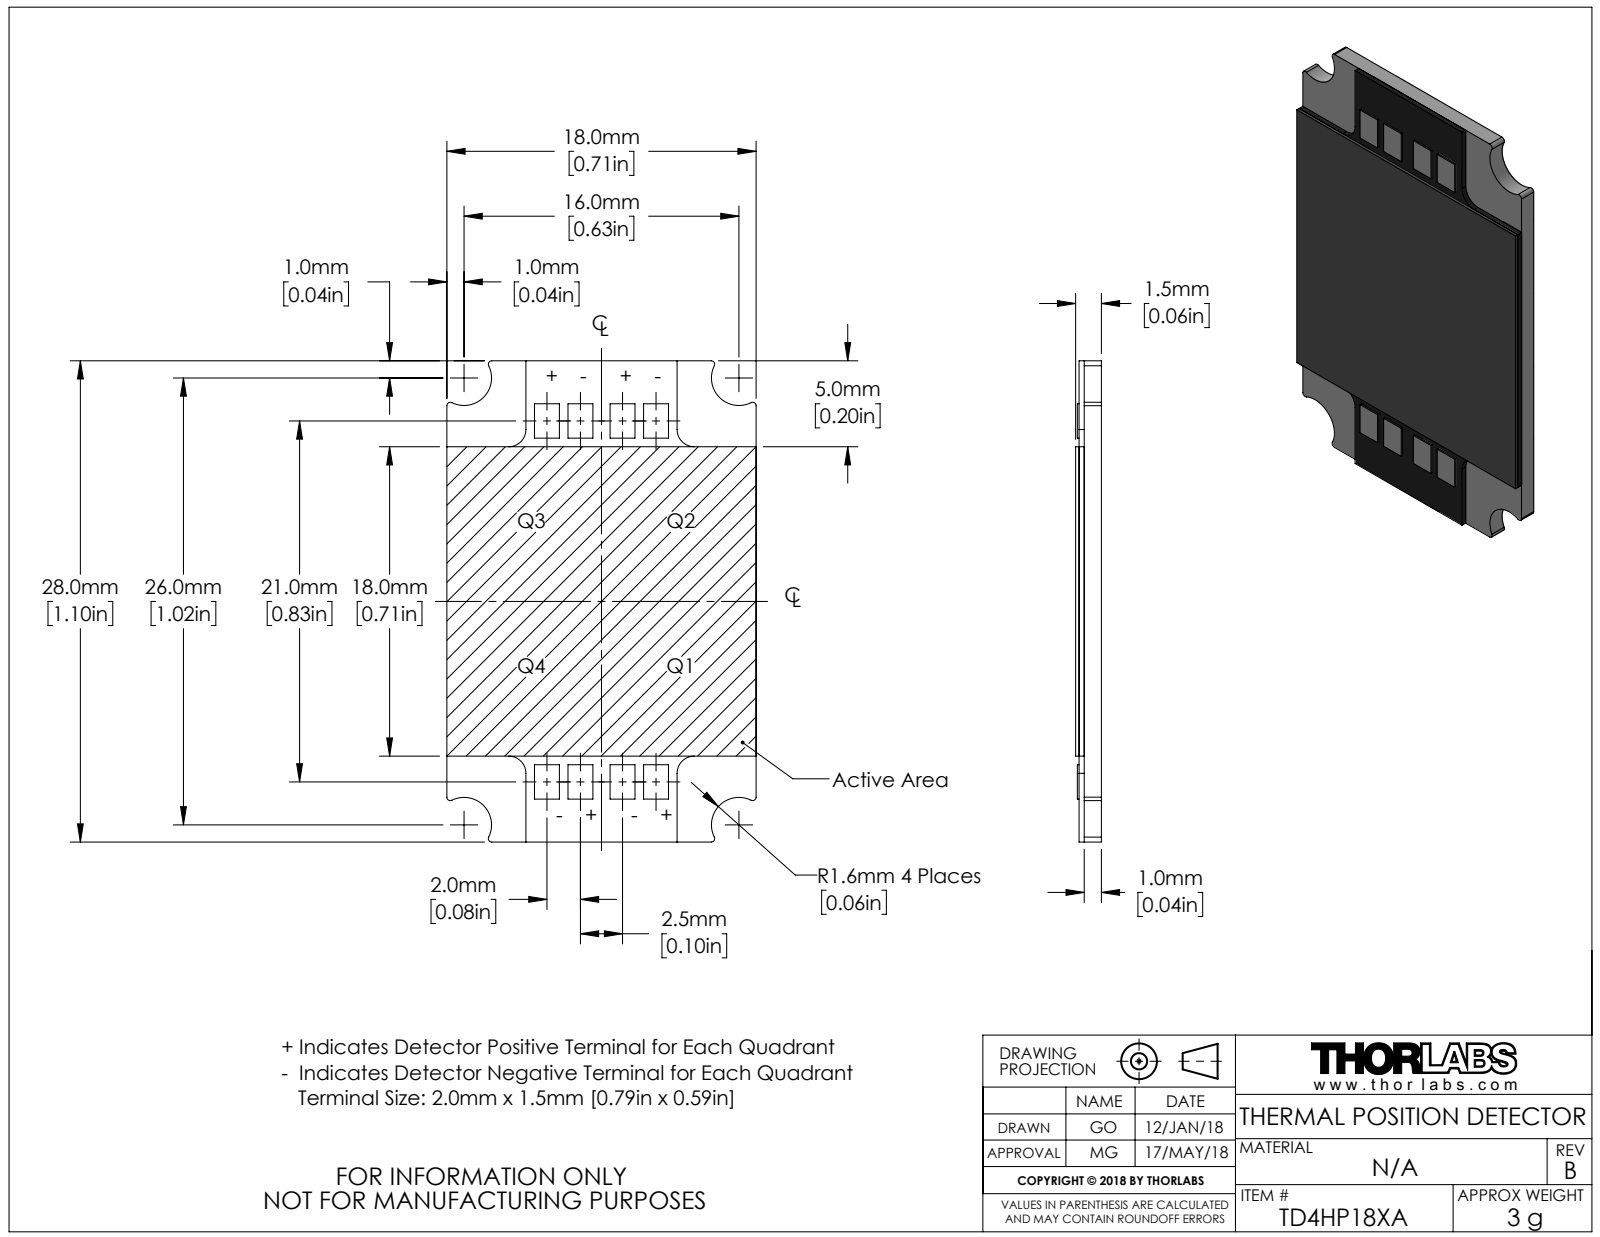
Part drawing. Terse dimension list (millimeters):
name: MTN11041-E0W
written by: SolidWorks 2016 (CONFIG_CONTROL_DESIGN)
unit: mm
bodies: 11 solids, 94 faces (74 planar, 20 cylindrical, 0 other)
size: 28 × 18 × 1.5
volume: 671 mm³; area: 2 617 mm²
rounds: 8× R0.2, 4× R1, 4× R1.6
face distances: 1, 1.3, 0.5, 1.5, 18, 1.4, 0.4, 28, 23, 5
